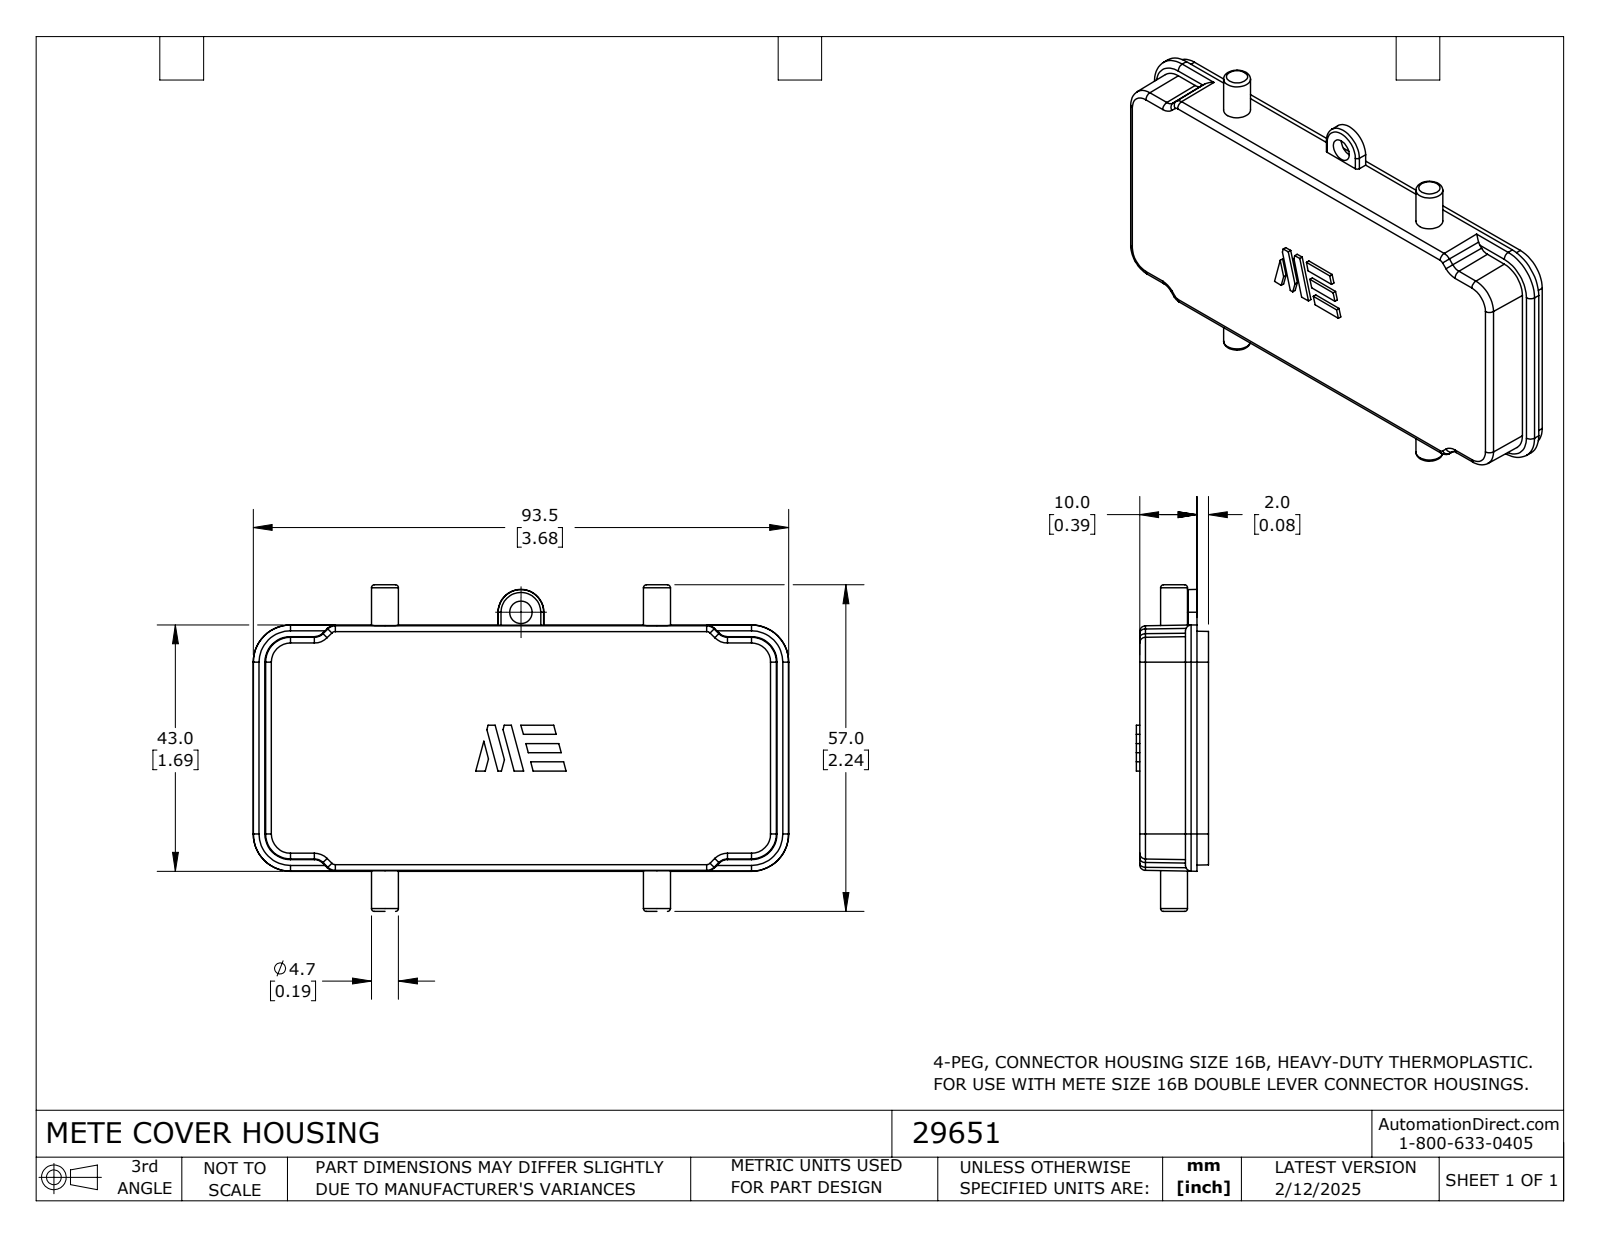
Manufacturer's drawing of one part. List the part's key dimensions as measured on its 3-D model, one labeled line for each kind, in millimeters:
Part name (STEP PRODUCT): 29651
STEP written by: SolidWorks 2024 (CONFIG_CONTROL_DESIGN)
Units: millimetres
Bodies: 1 solid, 196 faces (80 planar, 40 cylindrical, 76 other)
Overall size (bounding box): 93.5 × 57 × 12.6
Volume: 13 500 mm³ · Surface area: 13 680 mm²
Round bosses / shafts (diameter × count): ⌀4.7 ×2
Partial cylindrical surfaces — rounded edges, fillets, slot ends (radius × count): R1 ×14, R0.5 ×12
Main face-to-face distances: 2, 2.6, 10, 8, 1.7, 12, 41.9, 39.3, 1.1, 0.6
